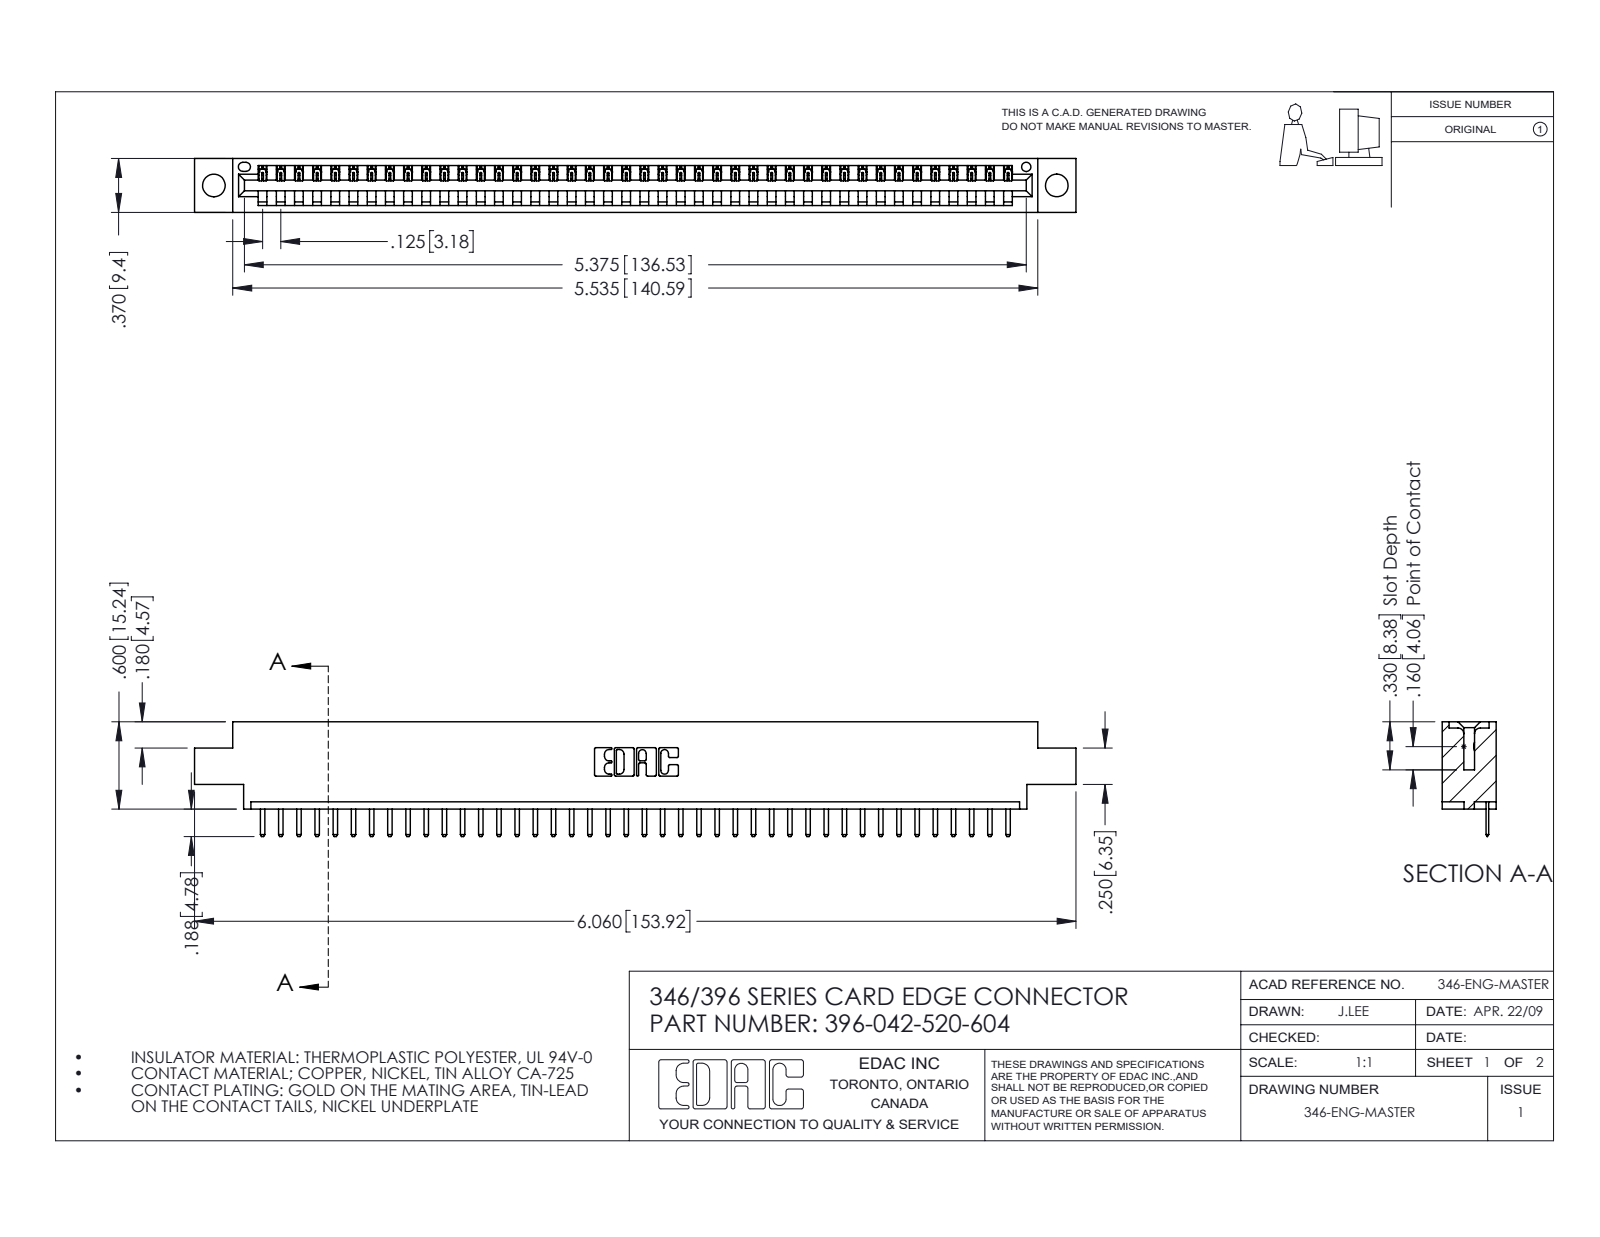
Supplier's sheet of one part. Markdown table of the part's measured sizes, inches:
| quantity | value |
| --- | --- |
| part name | 396-042-520-604; 346 Part_0.170 Offset - 0.156 Dia-TH; 345-292-001_345-293-120 |
| STEP written by | SolidWorks 2016 (CONFIG_CONTROL_DESIGN) |
| units | inches |
| bodies | 43 solids, 2730 faces (1844 planar, 886 cylindrical, 0 other) |
| overall size | 6.06 × 0.788 × 0.37 |
| volume | 0.877 in³ |
| surface area | 27.16 in² |
| round holes (diameter × count) | 0.156 × 2, 0.064 × 1 |
| partial cylindrical surfaces (radius × count) | 0.01 × 86, 0.006 × 84, 0.01 × 22, 0.007 × 6, 0.031 × 6, 0.026 × 3, 0.031 × 2, 0.04 × 2 |
| main face-to-face distances | 0.048, 0.322, 0.37, 0.25, 0.148, 0.222, 0.1, 0.174, 0.072, 0.298 |
| hole center spacings | 0.246, 5.586, 5.795 |
